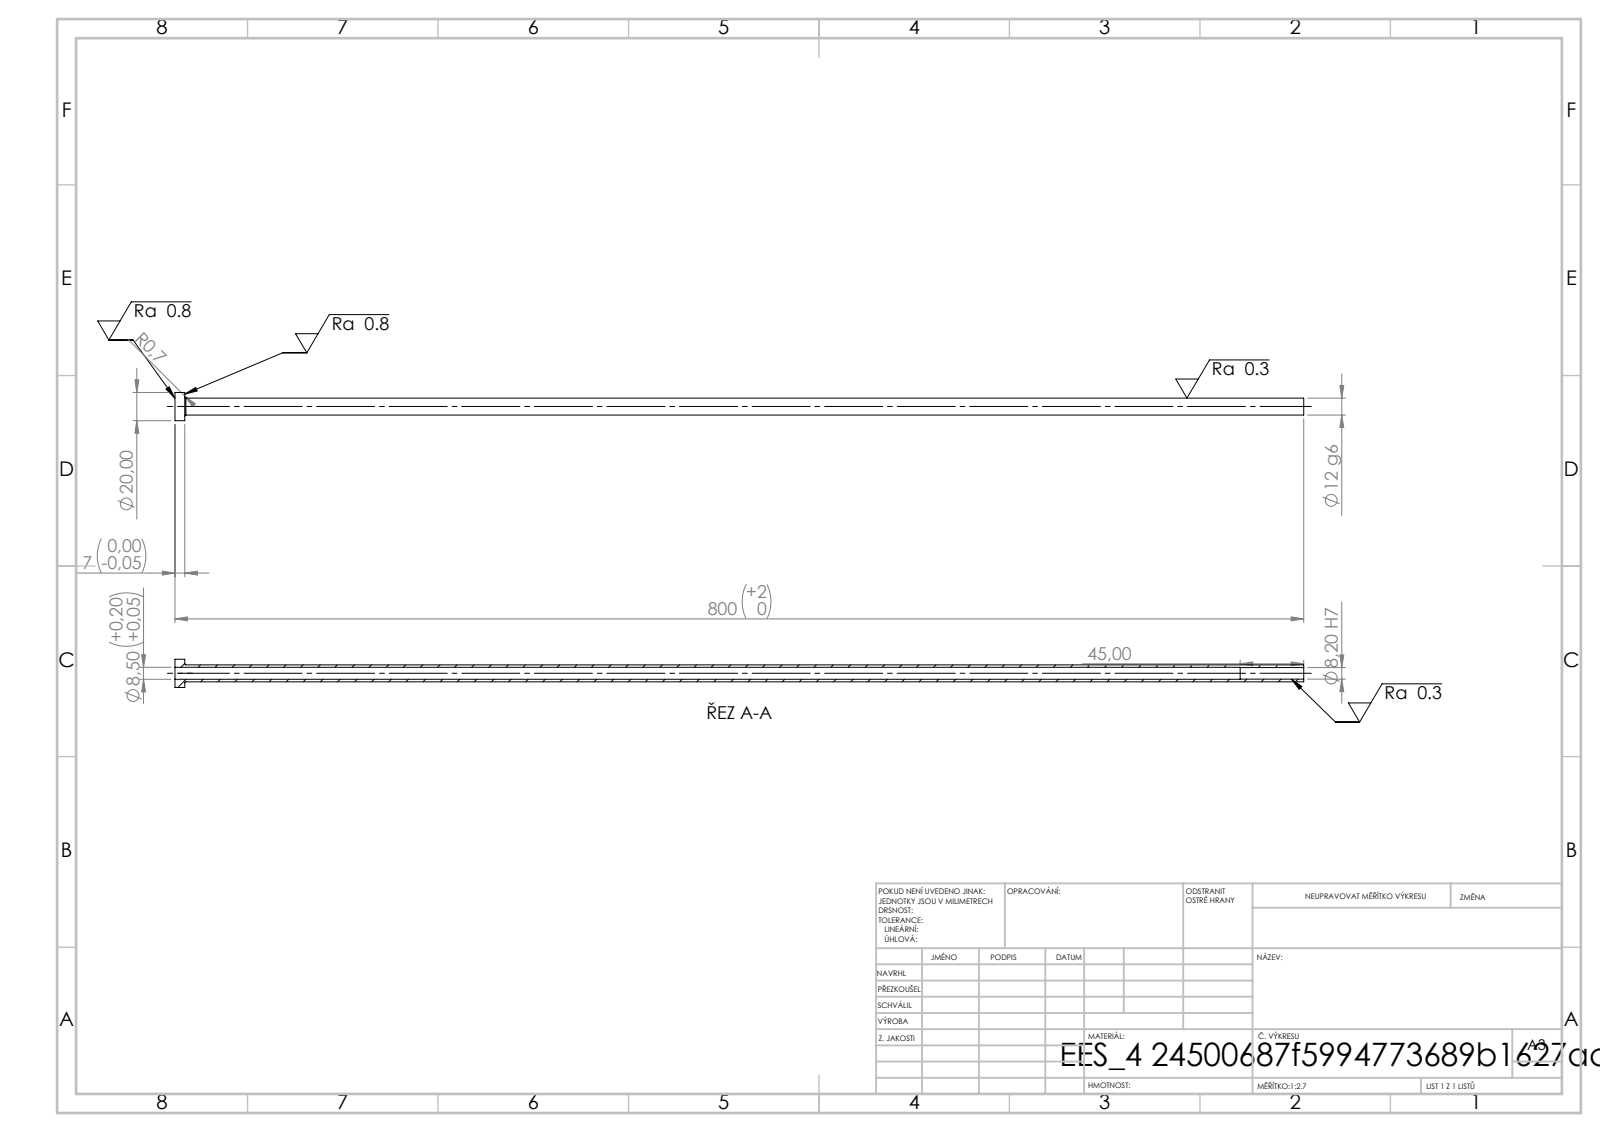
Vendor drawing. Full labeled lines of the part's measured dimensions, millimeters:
STEP written by: SolidWorks 2019 (CONFIG_CONTROL_DESIGN)
Units: millimetres
Bodies: 1 solid, 14 faces (4 planar, 8 cylindrical, 2 other)
Overall size (bounding box): 800 × 20 × 20
Volume: 46 670 mm³ · Surface area: 52 167 mm²
Round holes (diameter × count): ⌀8.2 ×1, ⌀8.5 ×1
Round bosses / shafts (diameter × count): ⌀20 ×1, ⌀12 ×1
Main face-to-face distances: 7, 800, 793, 755, 748, 45
